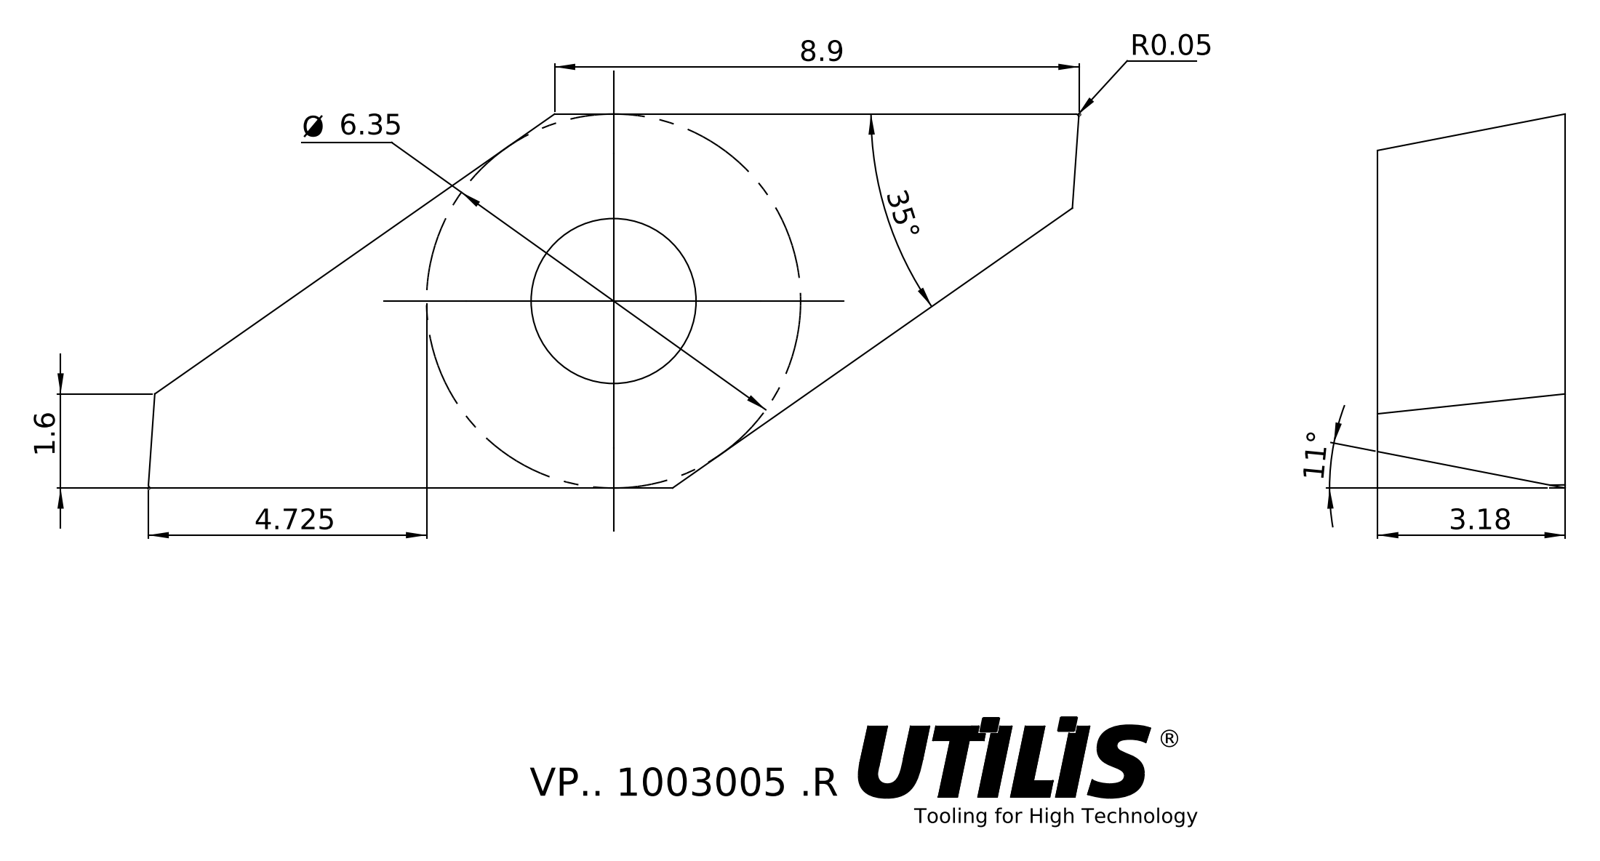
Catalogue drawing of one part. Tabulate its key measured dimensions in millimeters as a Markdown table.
| quantity | value |
| --- | --- |
| part name | VP.. 1003005 .R |
| STEP written by | SolidWorks 2016 (AUTOMOTIVE_DESIGN) |
| units | millimeters |
| bodies | 1 solid, 13 faces (8 planar, 2 cylindrical, 3 other) |
| overall size | 15.79 × 6.35 × 3.18 |
| volume | 158 mm³ |
| surface area | 242 mm² |
| round holes (diameter × count) | 2.8 × 1 |
| main face-to-face distances | 3.18 |
